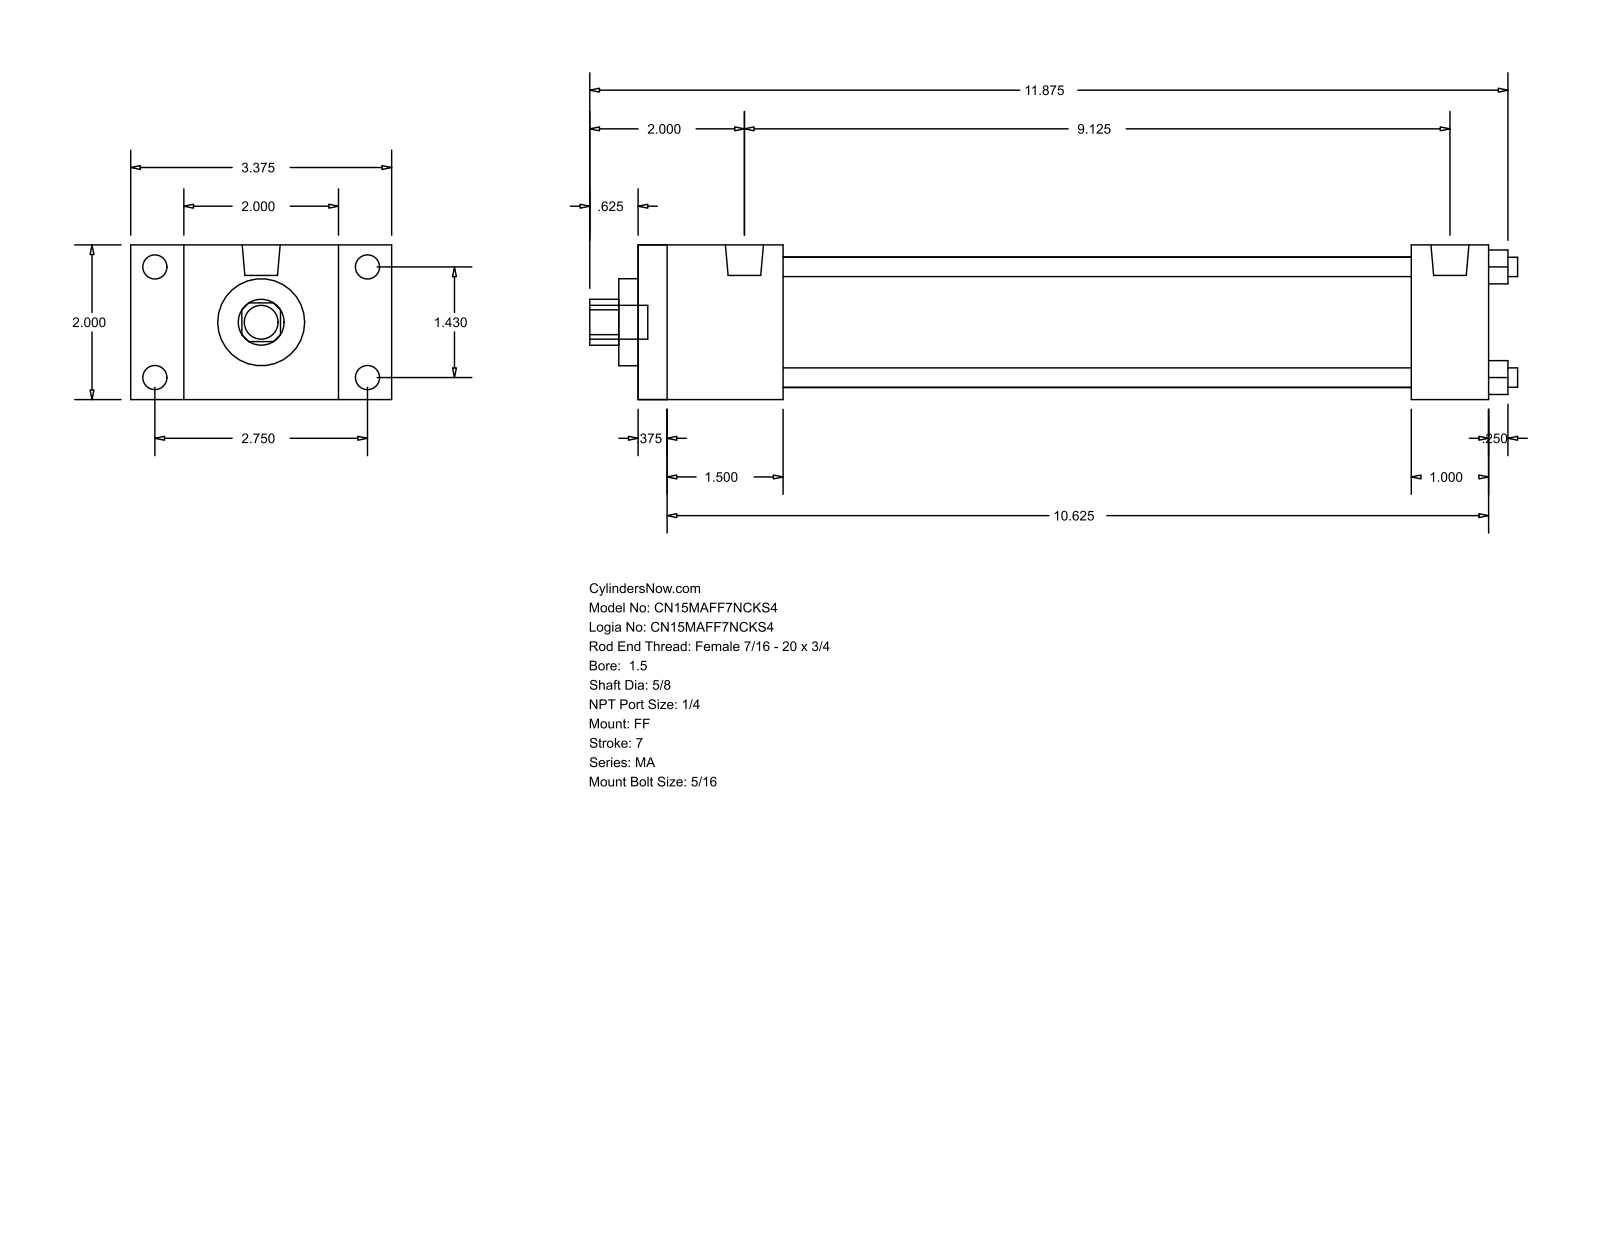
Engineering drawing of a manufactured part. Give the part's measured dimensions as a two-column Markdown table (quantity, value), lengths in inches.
| quantity | value |
| --- | --- |
| part name | MA_FF__0150_0.625 |
| STEP written by | GSSL Pune (CONFIG_CONTROL_DESIGN) |
| units | inches |
| bodies | 0 solids, 92 faces (64 planar, 28 cylindrical, 0 other) |
| overall size | 12 × 3.375 × 2 |
| round holes (diameter × count) | 0.25 × 4, 0.625 × 1, 1.125 × 1, 1.69 × 1 |
| round bosses / shafts (diameter × count) | 0.313 × 8, 0.492 × 2, 0.437 × 1 |
| partial cylindrical surfaces (radius × count) | 0.297 × 1 |
| main face-to-face distances | 2, 11, 0.375, 10.625, 1.875, 10, 1.5, 9.625, 8.125, 9.125 |
| hole center spacings | 1.011, 1.43, 2.022 |
